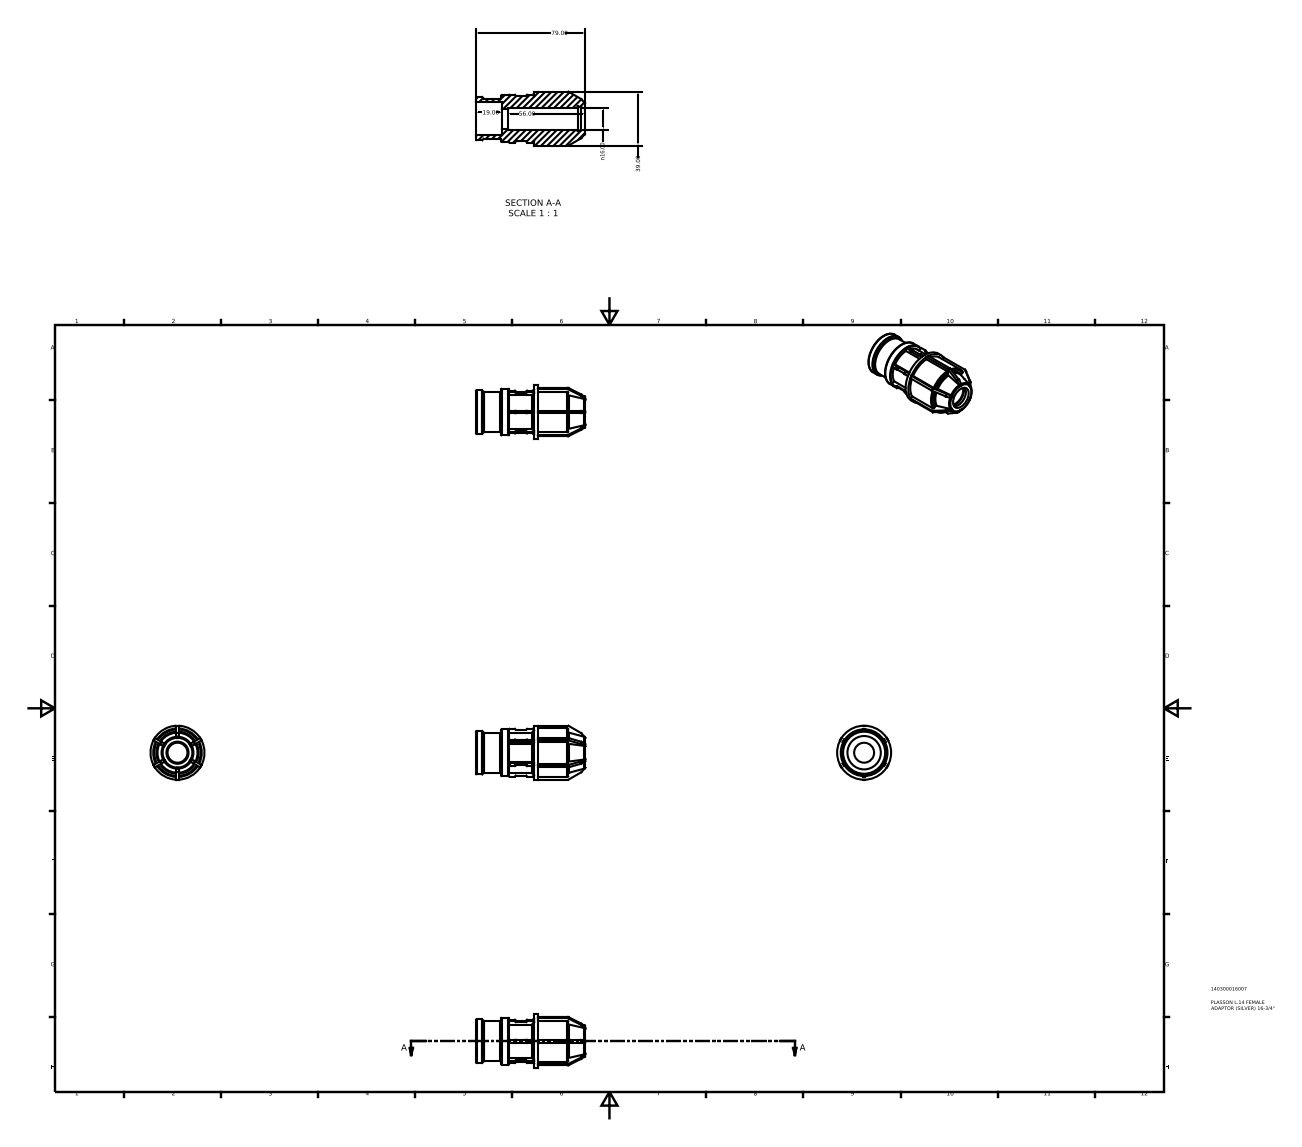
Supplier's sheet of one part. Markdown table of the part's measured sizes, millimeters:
| quantity | value |
| --- | --- |
| part name | 140300016007 |
| STEP written by | Autodesk Inventor 2015 (AUTOMOTIVE_DESIGN) |
| units | millimeters |
| bodies | 1 solid, 255 faces (159 planar, 68 cylindrical, 28 other) |
| overall size | 79 × 39 × 39 |
| volume | 41 536 mm³ |
| surface area | 15 859 mm² |
| round holes (diameter × count) | 14.4 × 1, 16 × 1, 24.12 × 1 |
| round bosses / shafts (diameter × count) | 39 × 1, 35.1 × 1, 33.76 × 1, 31.35 × 1, 28.94 × 1 |
| partial cylindrical surfaces (radius × count) | 0.48 × 48 |
| main face-to-face distances | 1.95, 1.94, 23.04, 19, 42.04, 1.96, 2.8, 4.85, 44.84, 25.84 |
